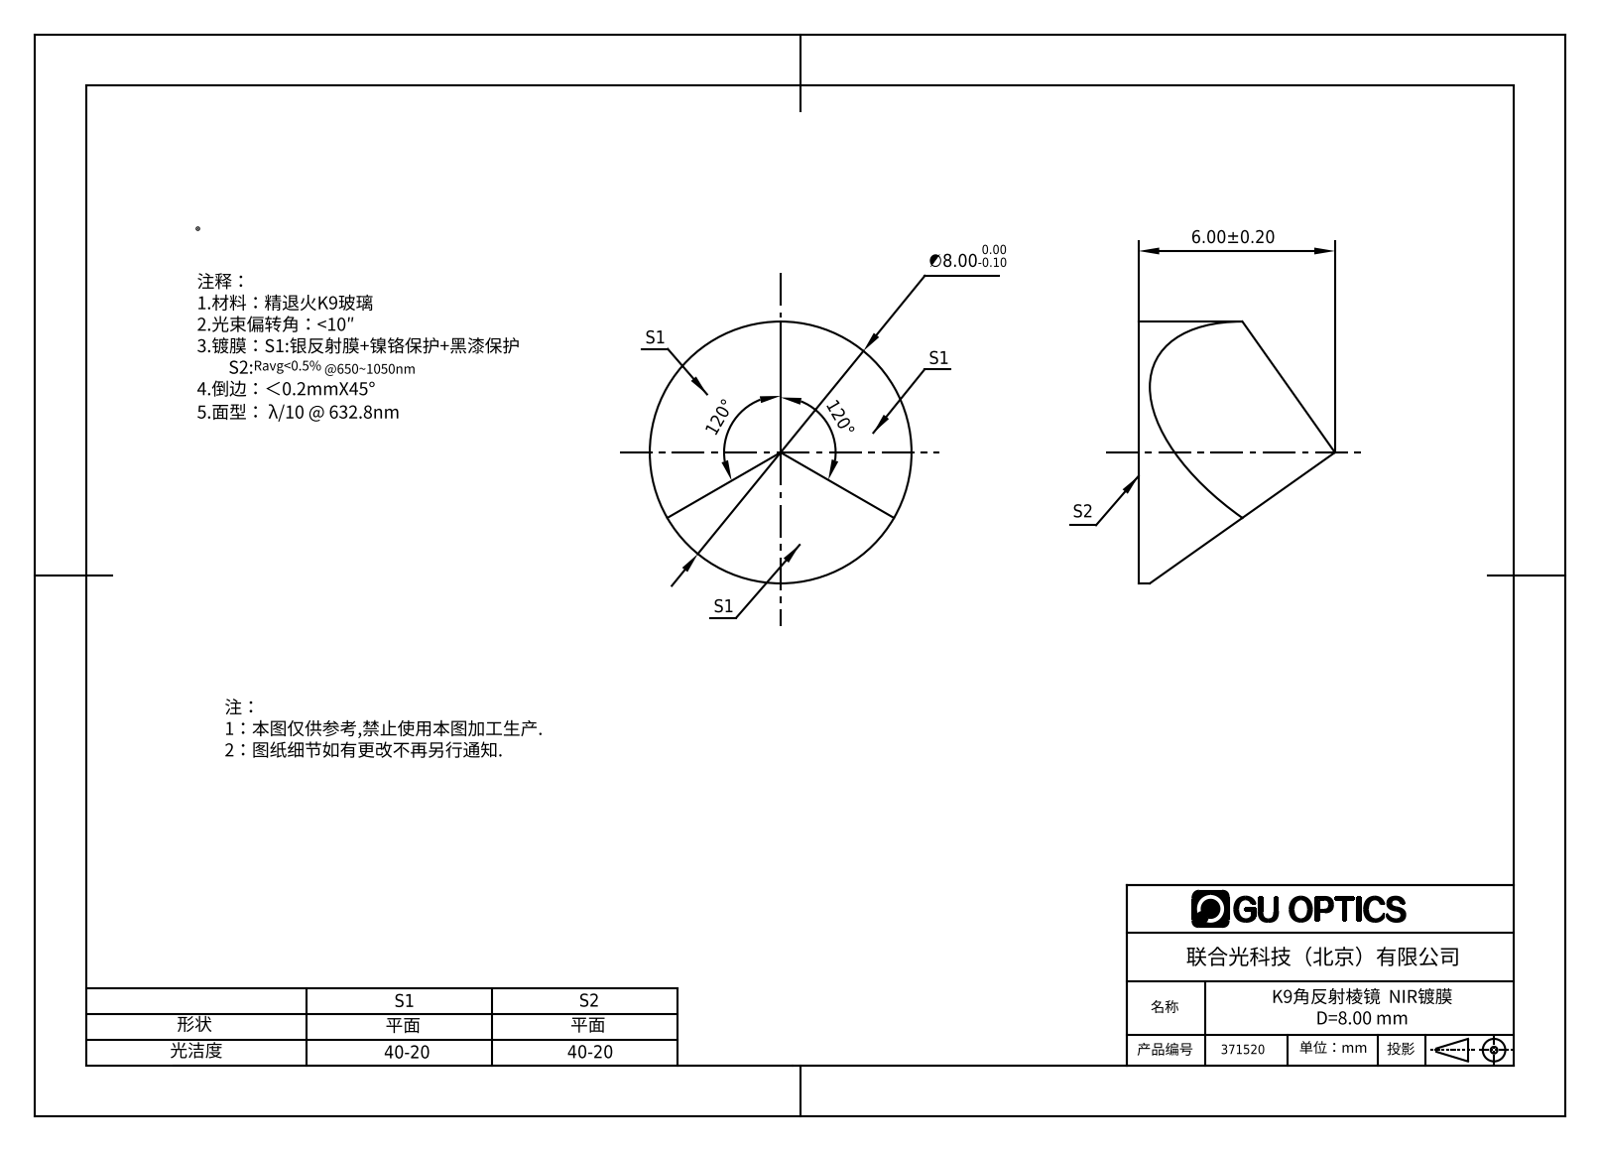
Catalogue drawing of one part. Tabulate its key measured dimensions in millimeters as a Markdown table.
| quantity | value |
| --- | --- |
| part name | 371500 |
| STEP written by | SolidWorks 2016 (CONFIG_CONTROL_DESIGN) |
| units | millimeters |
| bodies | 1 solid, 6 faces (4 planar, 2 cylindrical, 0 other) |
| overall size | 25.4 × 25.4 × 19 |
| volume | 4 611 mm³ |
| surface area | 1 715 mm² |
| round bosses / shafts (diameter × count) | 25.4 × 1 |
